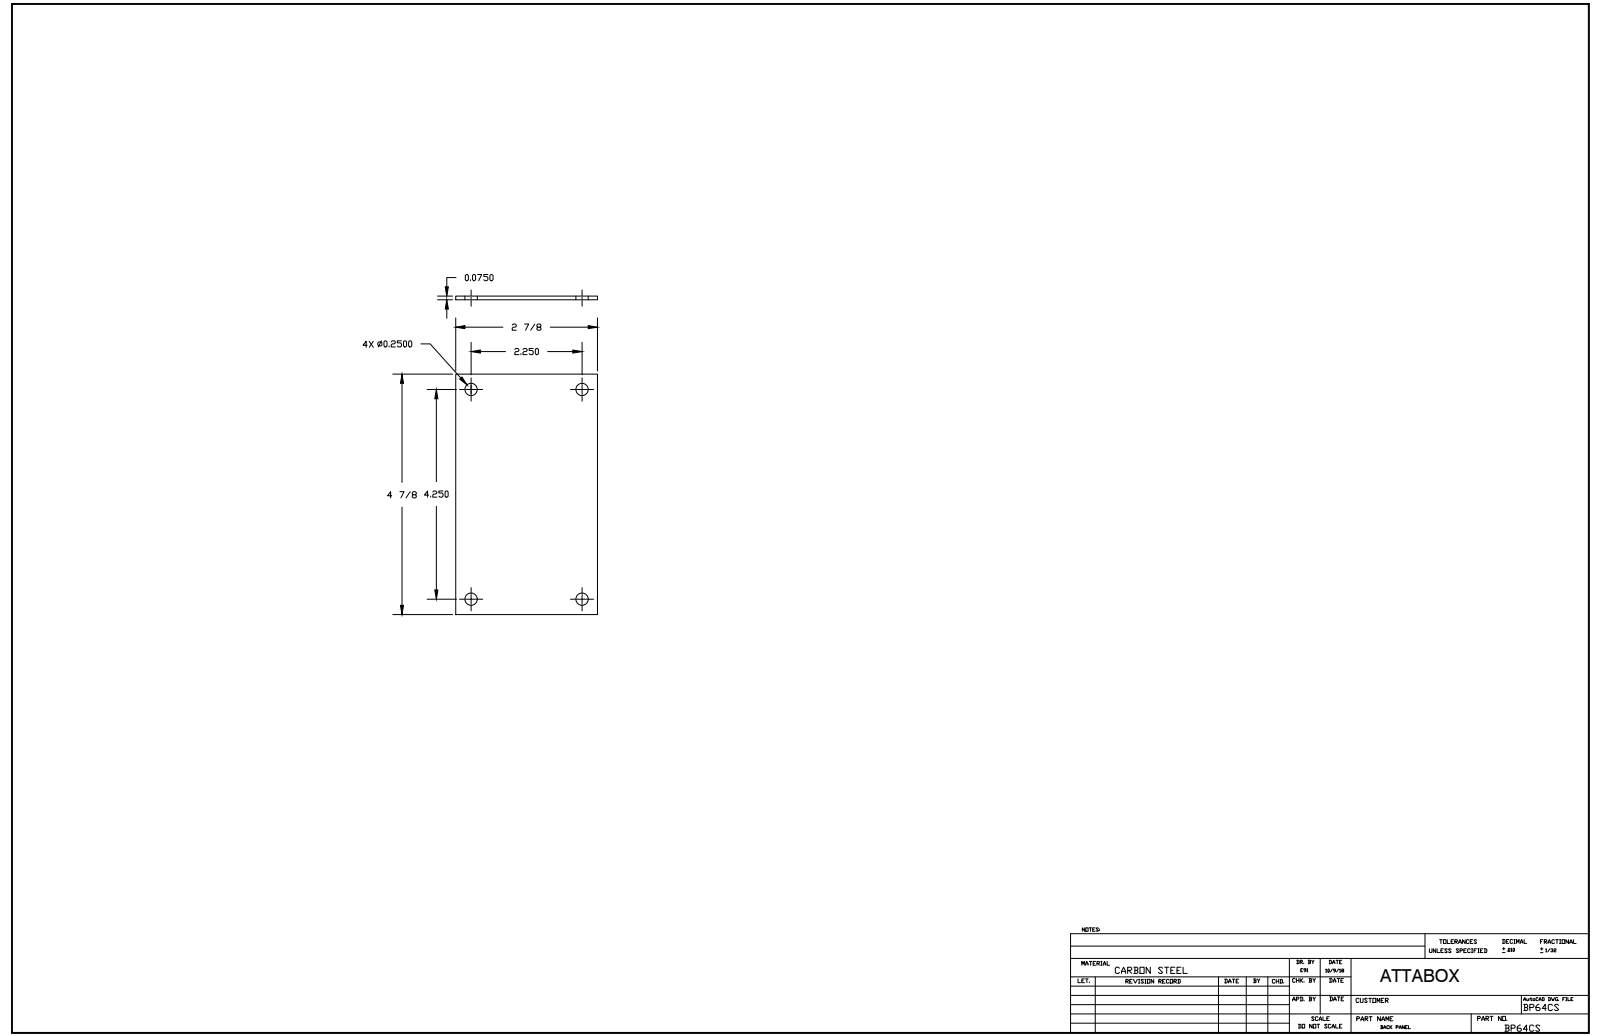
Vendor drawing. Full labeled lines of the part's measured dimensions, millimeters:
Part name (STEP PRODUCT): BP64CS_STP
STEP written by: Autodesk Inventor 2014 (AUTOMOTIVE_DESIGN)
Units: millimetres
Bodies: 1 solid, 10 faces (6 planar, 4 cylindrical, 0 other)
Overall size (bounding box): 123.95 × 73.15 × 1.91
Volume: 17 032 mm³ · Surface area: 18 784 mm²
Round holes (diameter × count): ⌀6.35 ×4
Main face-to-face distances: 1.9, 73.15, 123.95
Hole centre spacings: 57.15, 107.95, 122.14
